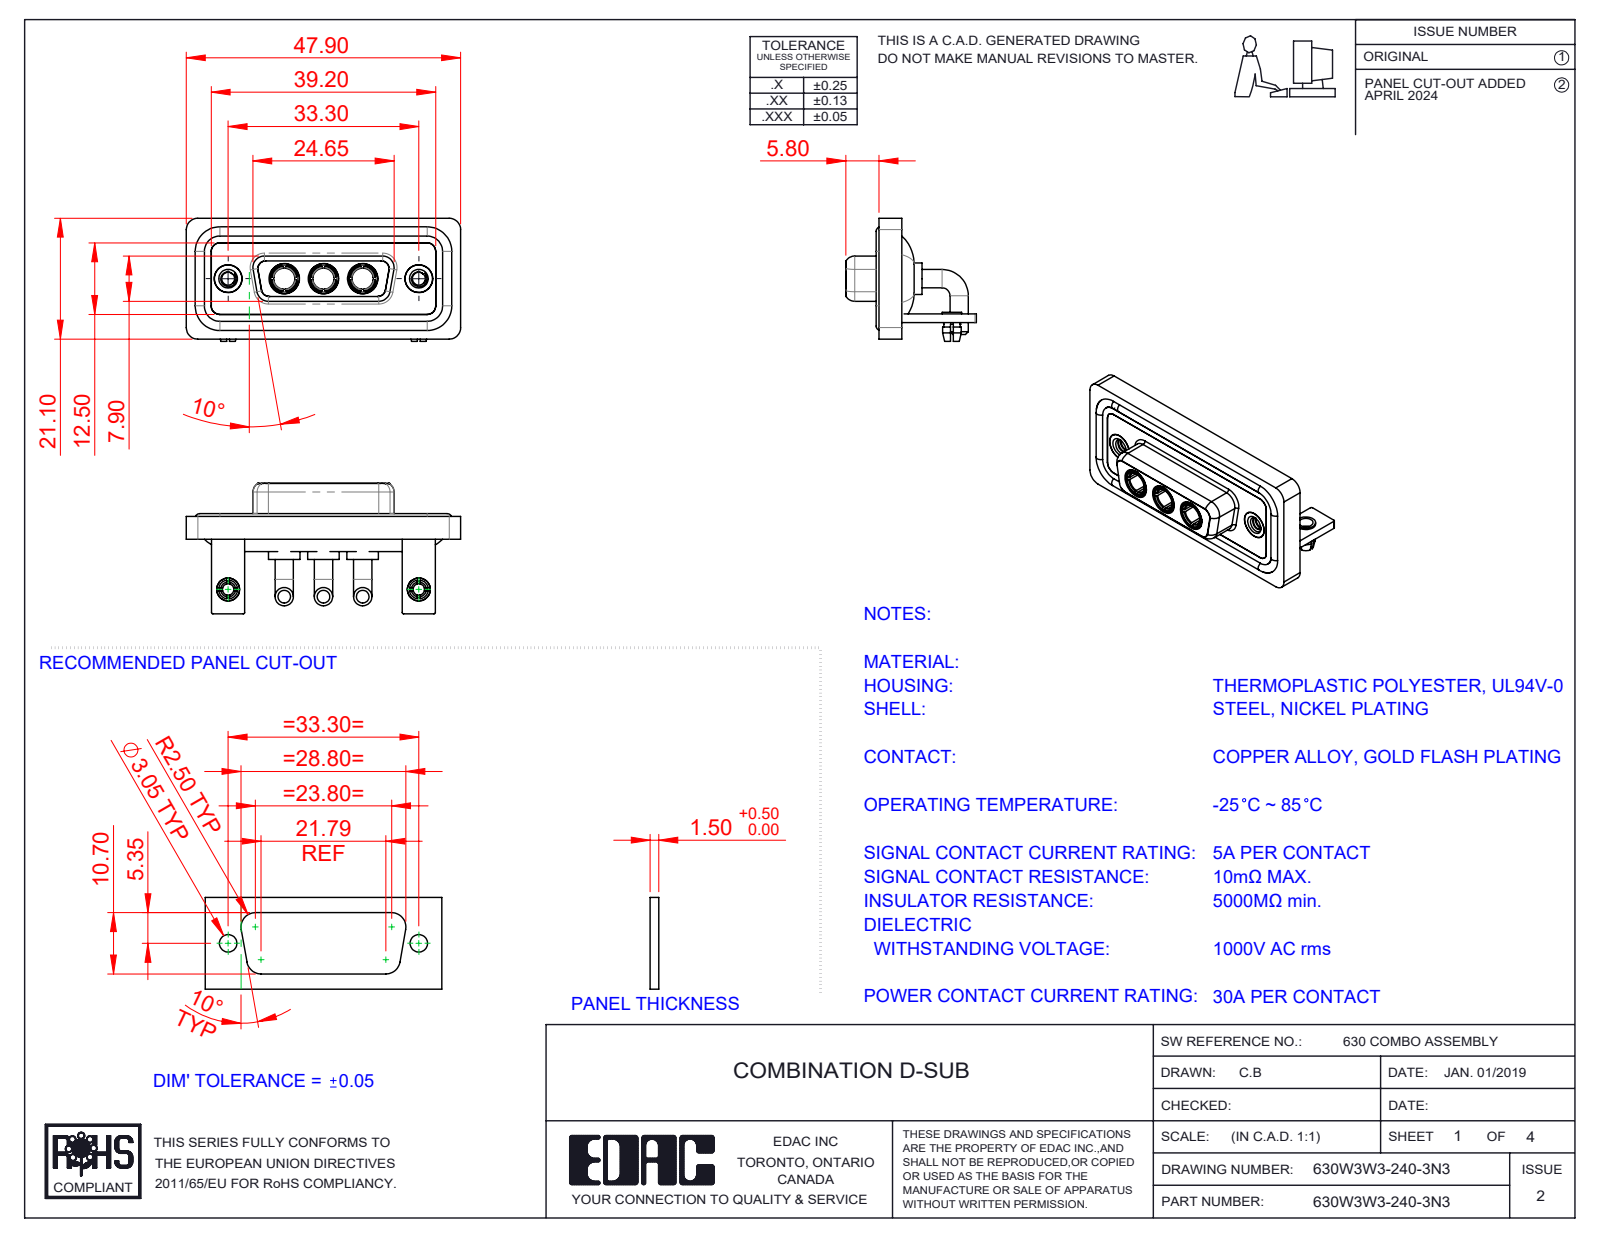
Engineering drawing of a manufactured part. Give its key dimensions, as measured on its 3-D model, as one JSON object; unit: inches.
{"part_name": "630Combo Stabilizer Bracket_50 Contacts; 630Combo Shell Rear_15 Contacts; 630Combo Waterproof Housing_15 Contacts; 630Combo Shell Front_15 Contacts (+5 more)", "step_written_by": "SolidWorks 2023 (CONFIG_CONTROL_DESIGN)", "units": "inches", "bodies": {"solids": 17, "faces": 760, "planar": 260, "cylindrical": 319, "other": 181}, "overall_size": [1.886, 0.898, 0.846], "volume_in3": 0.407, "surface_area_in2": 17.01, "round_holes": [[0.191, 5], [0.146, 3], [0.209, 3], [0.079, 2], [0.089, 2], [0.098, 2], [0.126, 2], [0.157, 2], [0.159, 2], [0.197, 2]], "round_bosses_or_shafts": [[0.126, 6], [0.063, 4], [0.217, 3], [0.205, 3], [0.195, 3], [0.187, 3], [0.148, 3], [0.195, 2]], "partial_cylinders_radius": [[0.079, 21], [0.059, 18], [0.01, 16], [0.053, 12], [0.063, 8], [0.02, 5], [0.024, 4], [0.026, 4]], "face_to_face_distances": [0.016, 0.114, 0.059, 0.071, 0.146, 0.043, 0.161, 0.063, 0.098, 0.055], "hole_center_spacings": [0.27, 0.386, 0.656, 0.925, 1.311, 0.539]}
